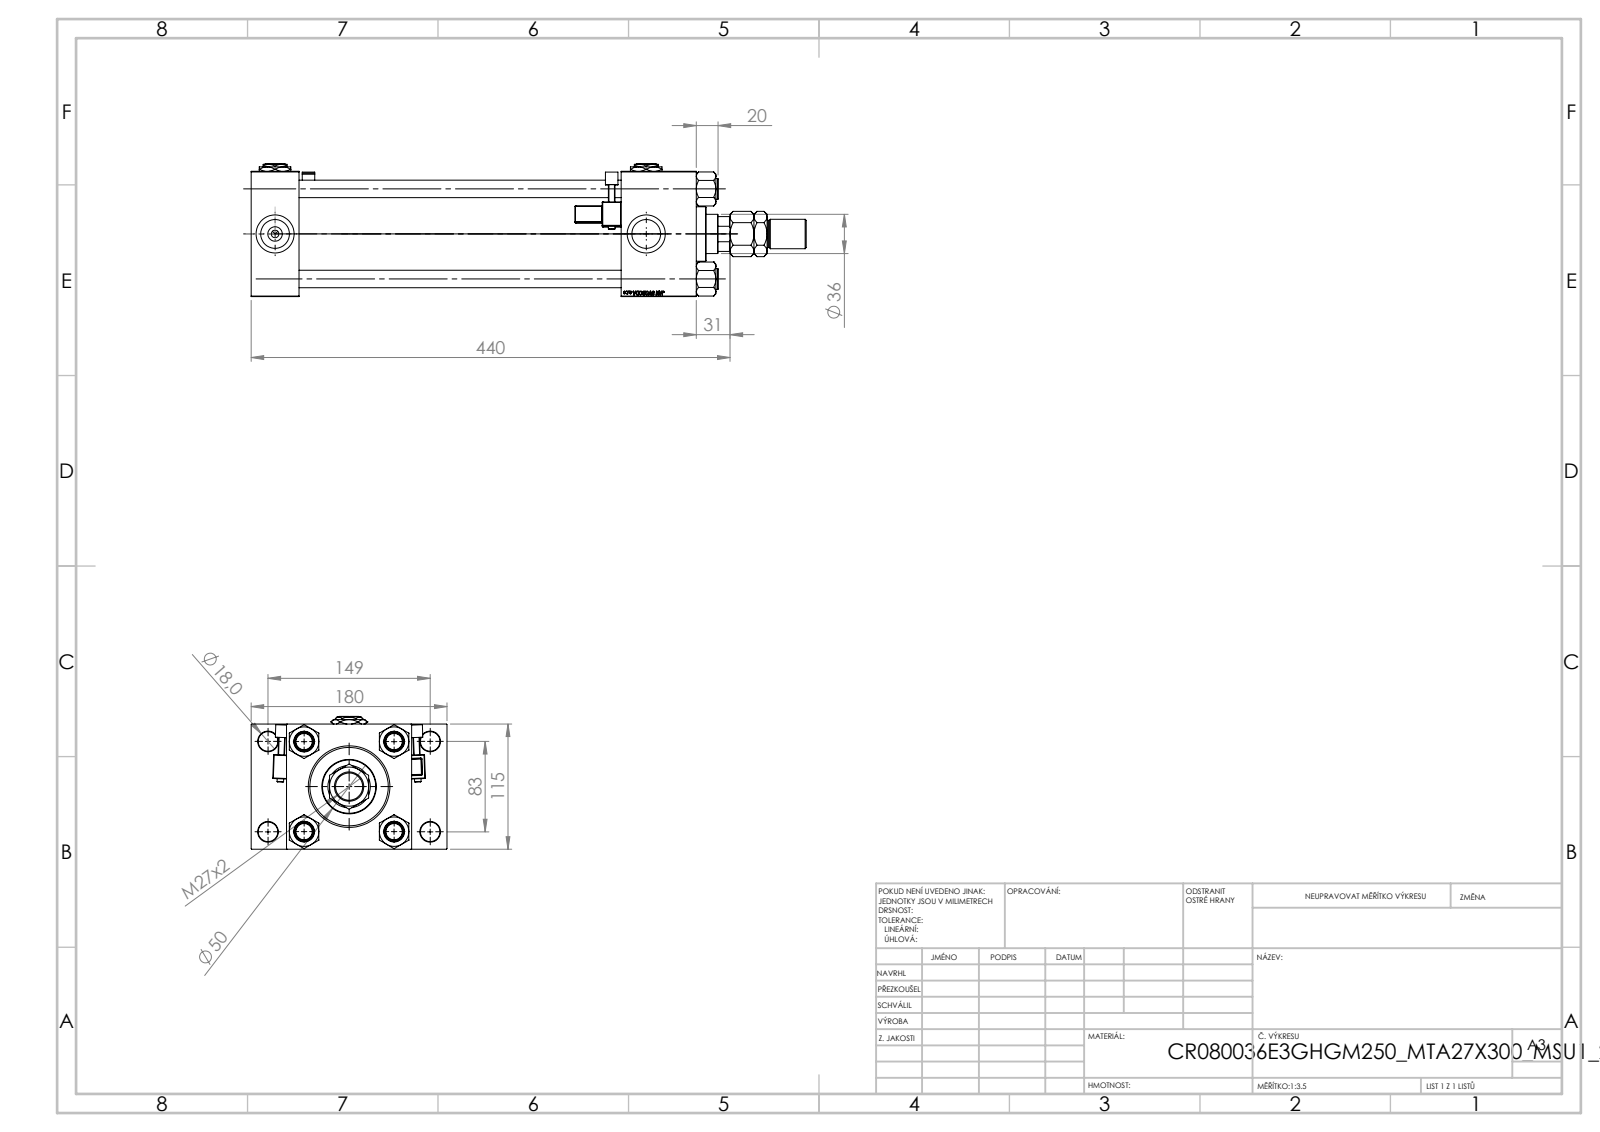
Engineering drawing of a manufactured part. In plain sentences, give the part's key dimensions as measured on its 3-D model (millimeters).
The part is named "V215_VC_A; V215CR_MSU; MTA; Zatka_pro_OIL_PORT (+4 more)". Its 3-D file was written by "SolidWorks 2019 (CONFIG_CONTROL_DESIGN)". It is 16 solids with 1493 faces: 668 planar, 165 cylindrical and 660 other. Overall it measures 510 by 180 by 122 millimeters. Its volume is 2 768 000 cubic millimeters and its surface area 531 495 square millimeters. Round holes: 4 of diameter 16, 4 of diameter 18, 4 of diameter 26.44, 4 of diameter 35, 3 of diameter 7, 2 of diameter 2.5, 1 of diameter 25.5, 1 of diameter 36, 1 of diameter 39, 1 of diameter 61, 1 of diameter 72, 1 of diameter 80. Round bosses or shafts: 4 of diameter 19, 2 of diameter 6, 1 of diameter 86, 1 of diameter 50, 1 of diameter 27, 1 of diameter 25. Partial cylindrical surfaces (rounded edges, fillets, slot ends): 48 of radius 0.5, 2 of radius 1, 2 of radius 2.5, 2 of radius 4, 1 of radius 17.5. The main face-to-face distances are 115, 44, 409, 365, 32.5, 340, 296, 69, 147.5, 90. The hole center spacings are 33.15, 41.96, 57.81, 58.48, 82.7, 85.28, 86.17, 89.24.
